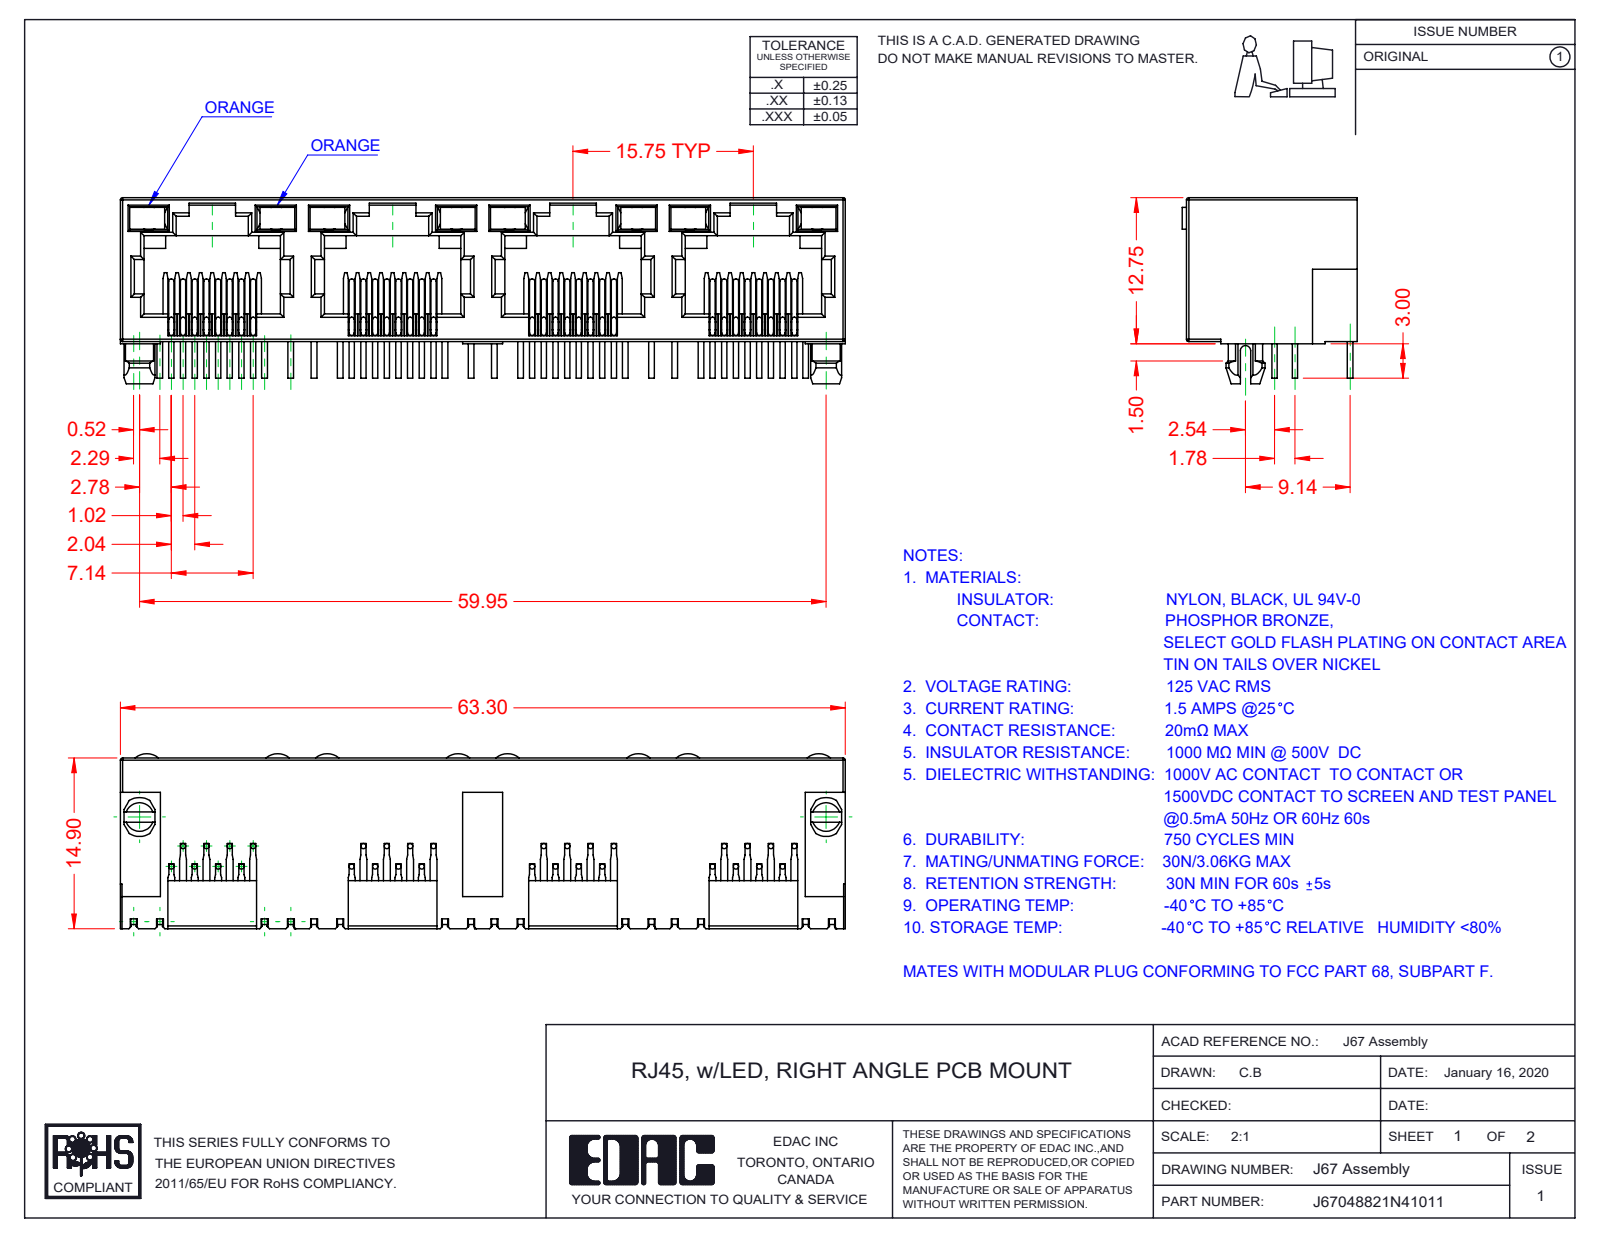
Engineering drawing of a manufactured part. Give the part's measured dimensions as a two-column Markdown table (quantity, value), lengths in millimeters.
| quantity | value |
| --- | --- |
| part name | 67 LED RH_4-Orange; J67048822N44011; 67 Contacts; 67 LED LH_4-Orange (+1 more) |
| STEP written by | SolidWorks 2016 (CONFIG_CONTROL_DESIGN) |
| units | millimeters |
| bodies | 41 solids, 2465 faces (1781 planar, 476 cylindrical, 208 other) |
| overall size | 63.3 × 16.25 × 15.28 |
| volume | 5 159 mm³ |
| surface area | 11 573 mm² |
| round bosses / shafts (diameter × count) | 0.46 × 96 |
| partial cylindrical surfaces (radius × count) | 0.2 × 66, 0.3 × 29, 0.45 × 9, 1.55 × 8, 1.5 × 2, 1.7 × 2, 0.35 × 1, 1 × 1 |
| main face-to-face distances | 0.5, 12.55, 1.89, 0.89, 10, 15.75, 1, 1.39, 11, 11.89 |
